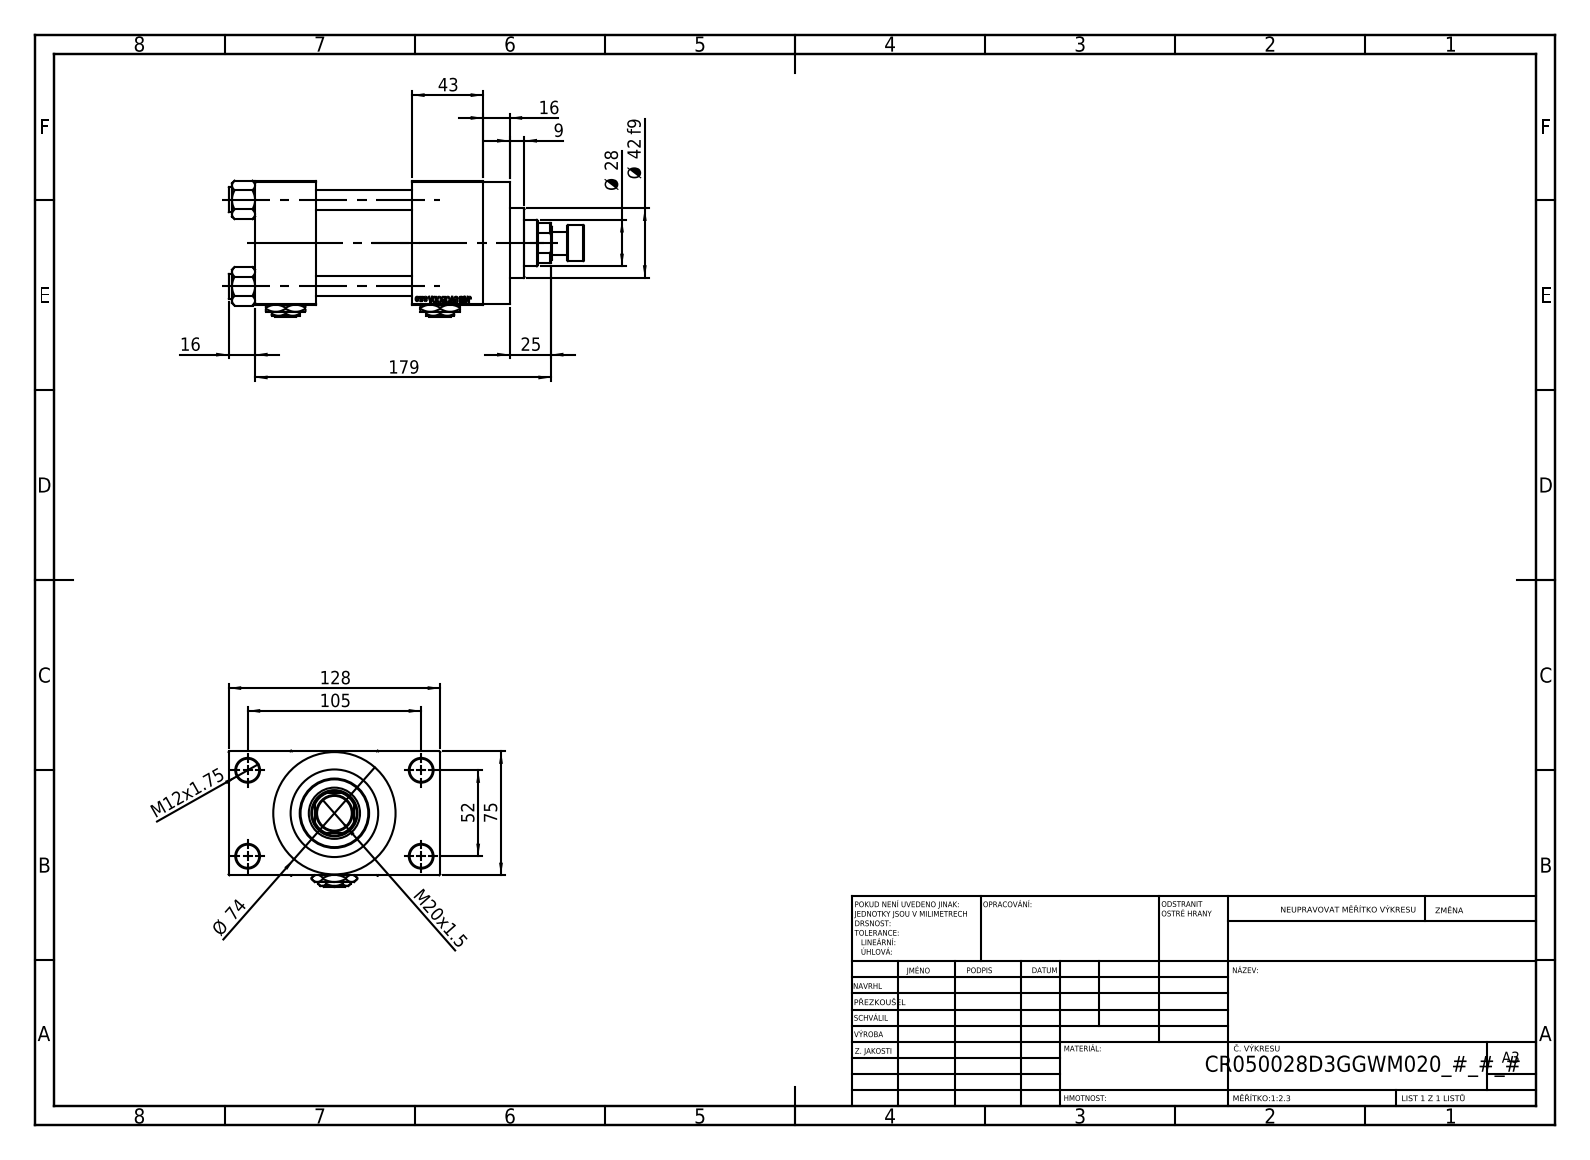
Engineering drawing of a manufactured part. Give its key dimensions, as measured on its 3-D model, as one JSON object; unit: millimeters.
{"part_name": "V215CR_D_TYCINKA; V215CR_D_Body; V215CR_VCP_D; Zatka_pro_OIL_PORT (+3 more)", "step_written_by": "SolidWorks 2019 (CONFIG_CONTROL_DESIGN)", "units": "millimeters", "bodies": {"solids": 14, "faces": 1219, "planar": 549, "cylindrical": 104, "other": 566}, "overall_size": [215, 128, 82.27], "volume_mm3": 816290, "surface_area_mm2": 175342, "round_holes": [[12, 4], [14, 4], [7, 2], [20.96, 2], [30, 2], [18.5, 1], [28, 1], [31, 1], [41, 1], [50, 1], [53, 1]], "round_bosses_or_shafts": [[15, 4], [74, 1], [56, 1], [42, 1], [22, 1], [14, 1]], "partial_cylinders_radius": [[13.5, 1]], "face_to_face_distances": [75, 58, 37, 95, 26.5, 101.5, 138, 101, 43, 16], "hole_center_spacings": [26.35, 36.98, 52.3, 58.43, 58.59, 78.65, 94.37, 52]}
